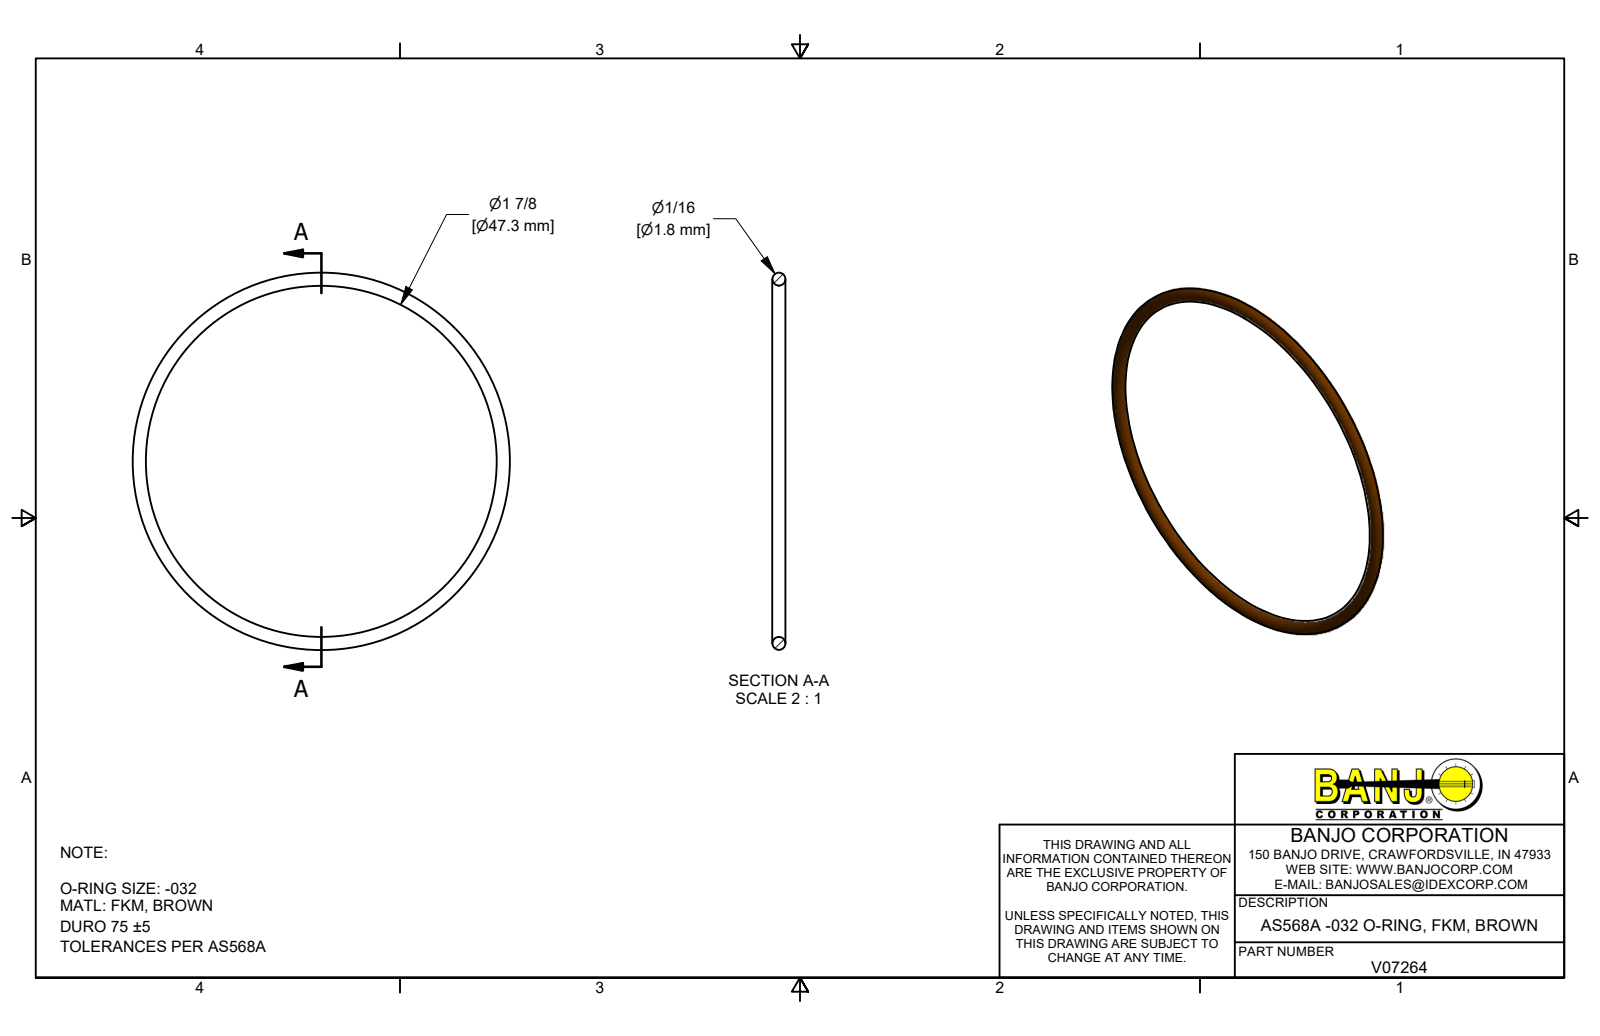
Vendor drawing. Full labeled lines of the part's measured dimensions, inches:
Part name (STEP PRODUCT): V07264
STEP written by: Autodesk Inventor 2019 (AUTOMOTIVE_DESIGN)
Units: inches
Bodies: 1 solid, 1 faces (0 planar, 0 cylindrical, 1 other)
Overall size (bounding box): 2.004 × 2.004 × 0.07
Volume: 0.023 in³ · Surface area: 1.336 in²
